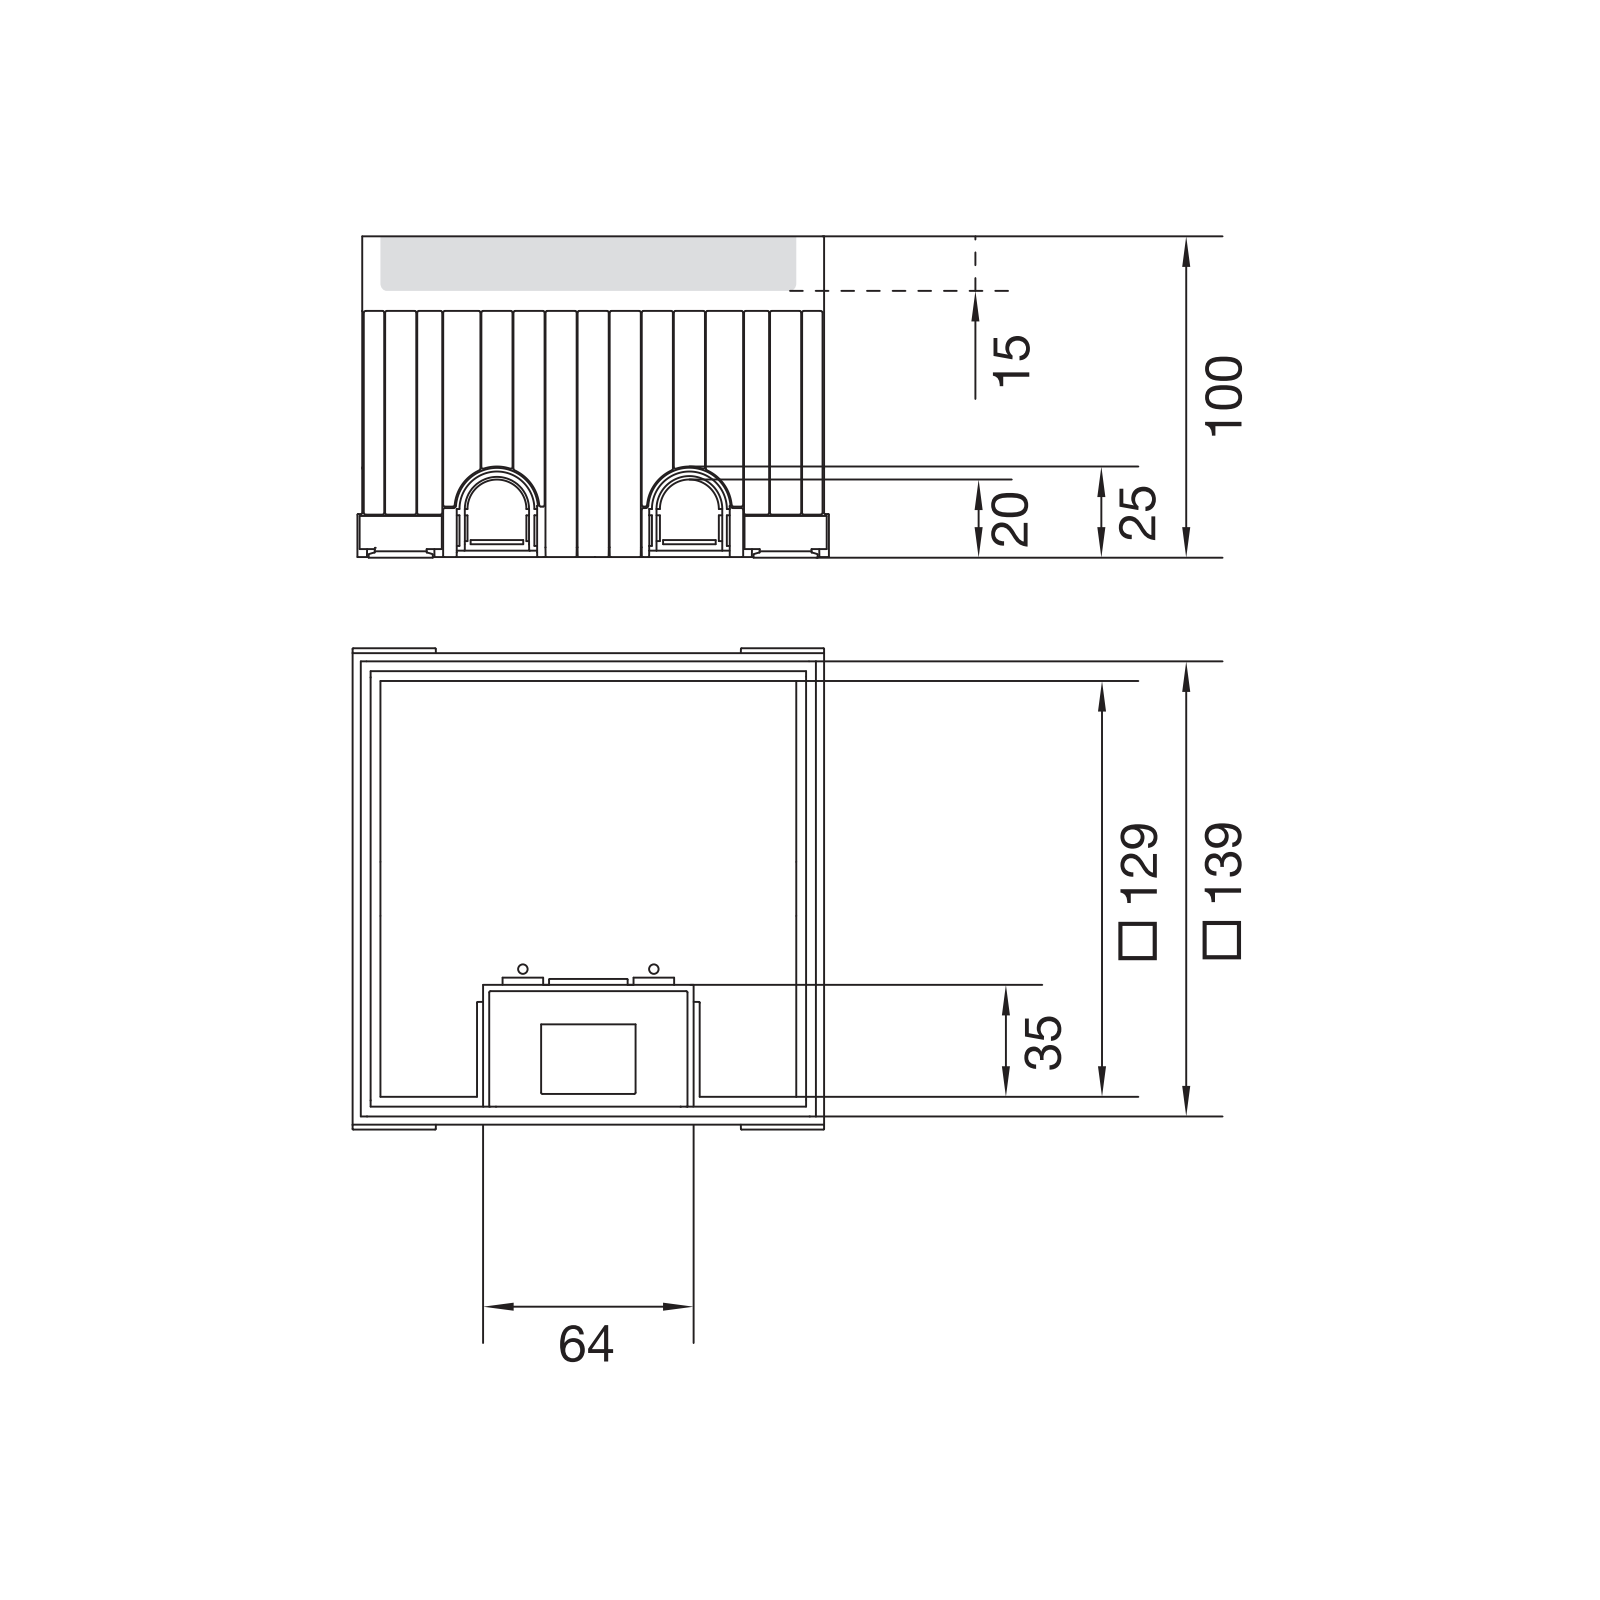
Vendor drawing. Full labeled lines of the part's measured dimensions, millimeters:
Part name (STEP PRODUCT): T-01523; 60449-M; 60450-M; T-01524KON (+8 more)
STEP written by: CREO PARAMETRIC BY PTC INC, 2022024 (AUTOMOTIVE_DESIGN)
Units: millimetres
Bodies: 26 solids, 1463 faces (857 planar, 378 cylindrical, 228 other)
Overall size (bounding box): 147 × 144 × 100.2
Volume: 286 643 mm³ · Surface area: 359 230 mm²
Round holes (diameter × count): ⌀2.4 ×4, ⌀6.8 ×4, ⌀7.5 ×4, ⌀10 ×4, ⌀12 ×4, ⌀18.5 ×4, ⌀6.5 ×3
Round bosses / shafts (diameter × count): ⌀20.5 ×4, ⌀20 ×4, ⌀11.5 ×4, ⌀9.85 ×4, ⌀8.5 ×4, ⌀8 ×4, ⌀10 ×1
Partial cylindrical surfaces — rounded edges, fillets, slot ends (radius × count): R0.2 ×92, R5 ×21, R1 ×12, R10 ×10, R3 ×8, R10.25 ×8, R12.5 ×8, R12.75 ×8
Main face-to-face distances: 1.5, 3, 2, 136.5, 139.5, 138, 135, 5, 141, 4.5
Hole centre spacings: 13.58, 53.82, 63.25, 80.75, 84.85, 107.63, 115.52, 116.62
